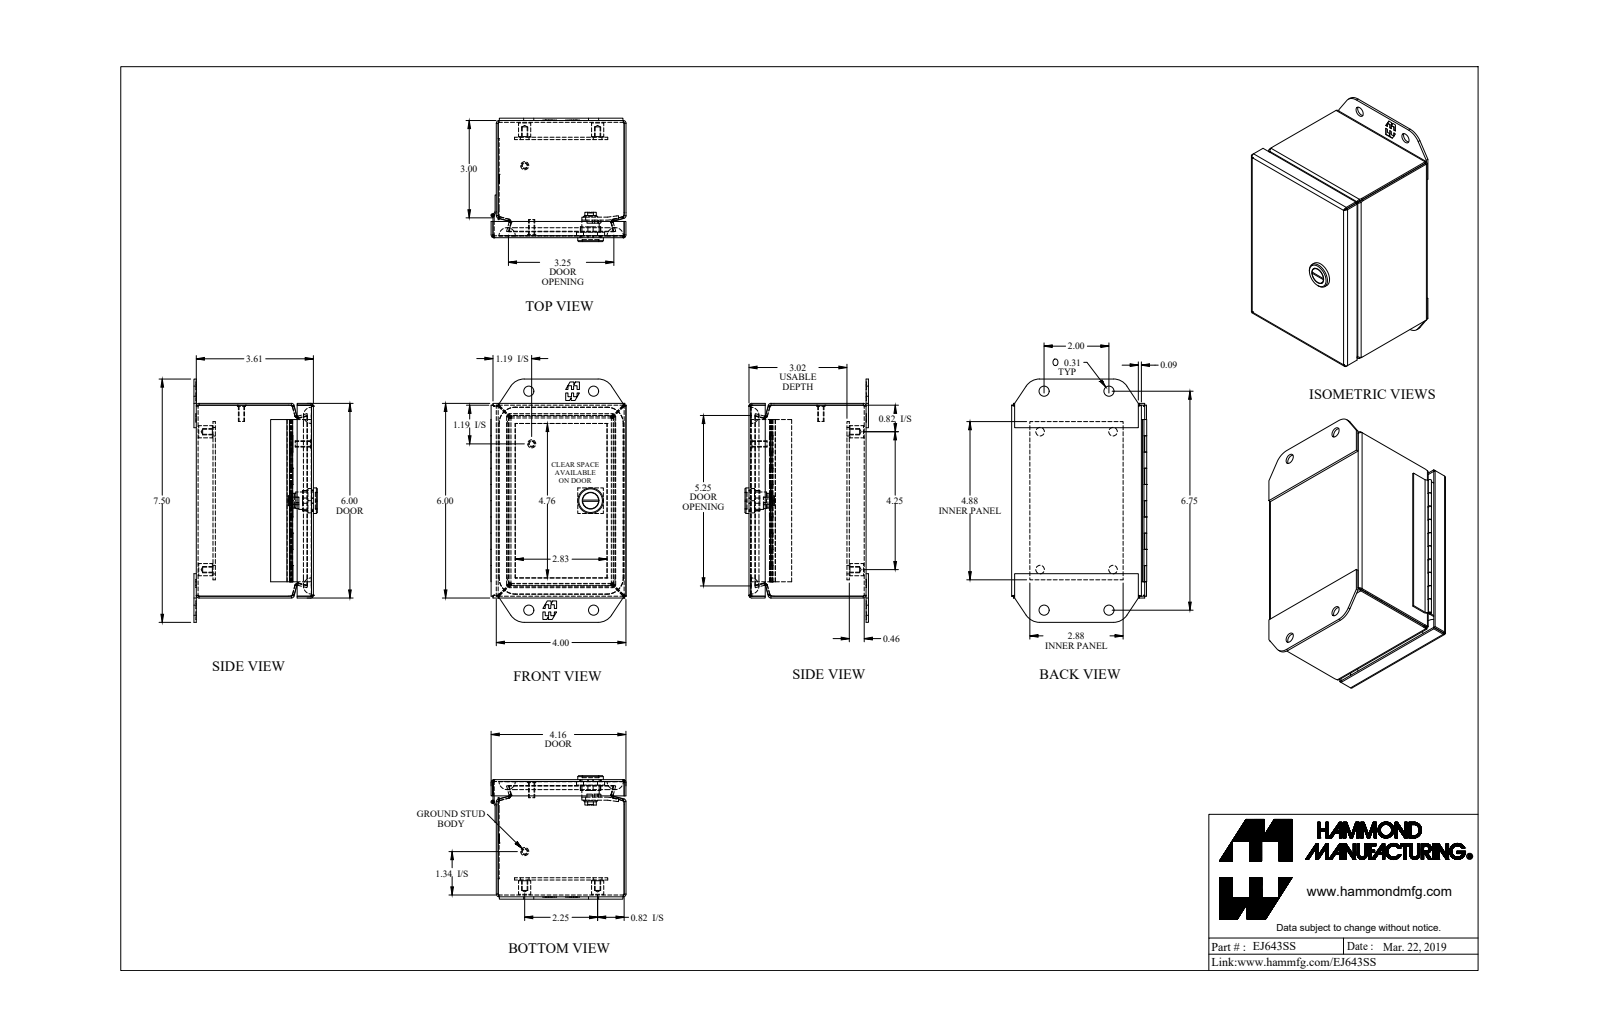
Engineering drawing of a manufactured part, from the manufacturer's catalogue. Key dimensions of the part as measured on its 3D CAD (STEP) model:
Part name (STEP PRODUCT): EJ643SS_Default
STEP written by: SolidWorks 2019 (CONFIG_CONTROL_DESIGN)
Units: inches
Bodies: 16 solids, 624 faces (354 planar, 174 cylindrical, 96 other)
Overall size (bounding box): 7.5 × 4.165 × 3.805
Volume: 11.29 in³ · Surface area: 370.6 in²
Round holes (diameter × count): ⌀0.156 ×4, ⌀0.265 ×4, ⌀0.313 ×4, ⌀0.05 ×1, ⌀0.516 ×1
Round bosses / shafts (diameter × count): ⌀0.375 ×4, ⌀0.25 ×2, ⌀0.19 ×2, ⌀0.788 ×1, ⌀0.535 ×1, ⌀0.496 ×1, ⌀0.435 ×1, ⌀0.1 ×1
Partial cylindrical surfaces — rounded edges, fillets, slot ends (radius × count): R0.029 ×16, R0.086 ×16, R0.281 ×12, R0.25 ×4, R0.499 ×4, R0.5 ×4, R0.06 ×2, R0.03 ×1
Main face-to-face distances: 0.057, 3.554, 3.943, 5.943, 0.072, 0.589, 3.611, 3.497, 3.886, 4
Hole centre spacings: 1.257, 5.502, 4.25, 2.465, 2.94, 5.896, 2, 2.136
